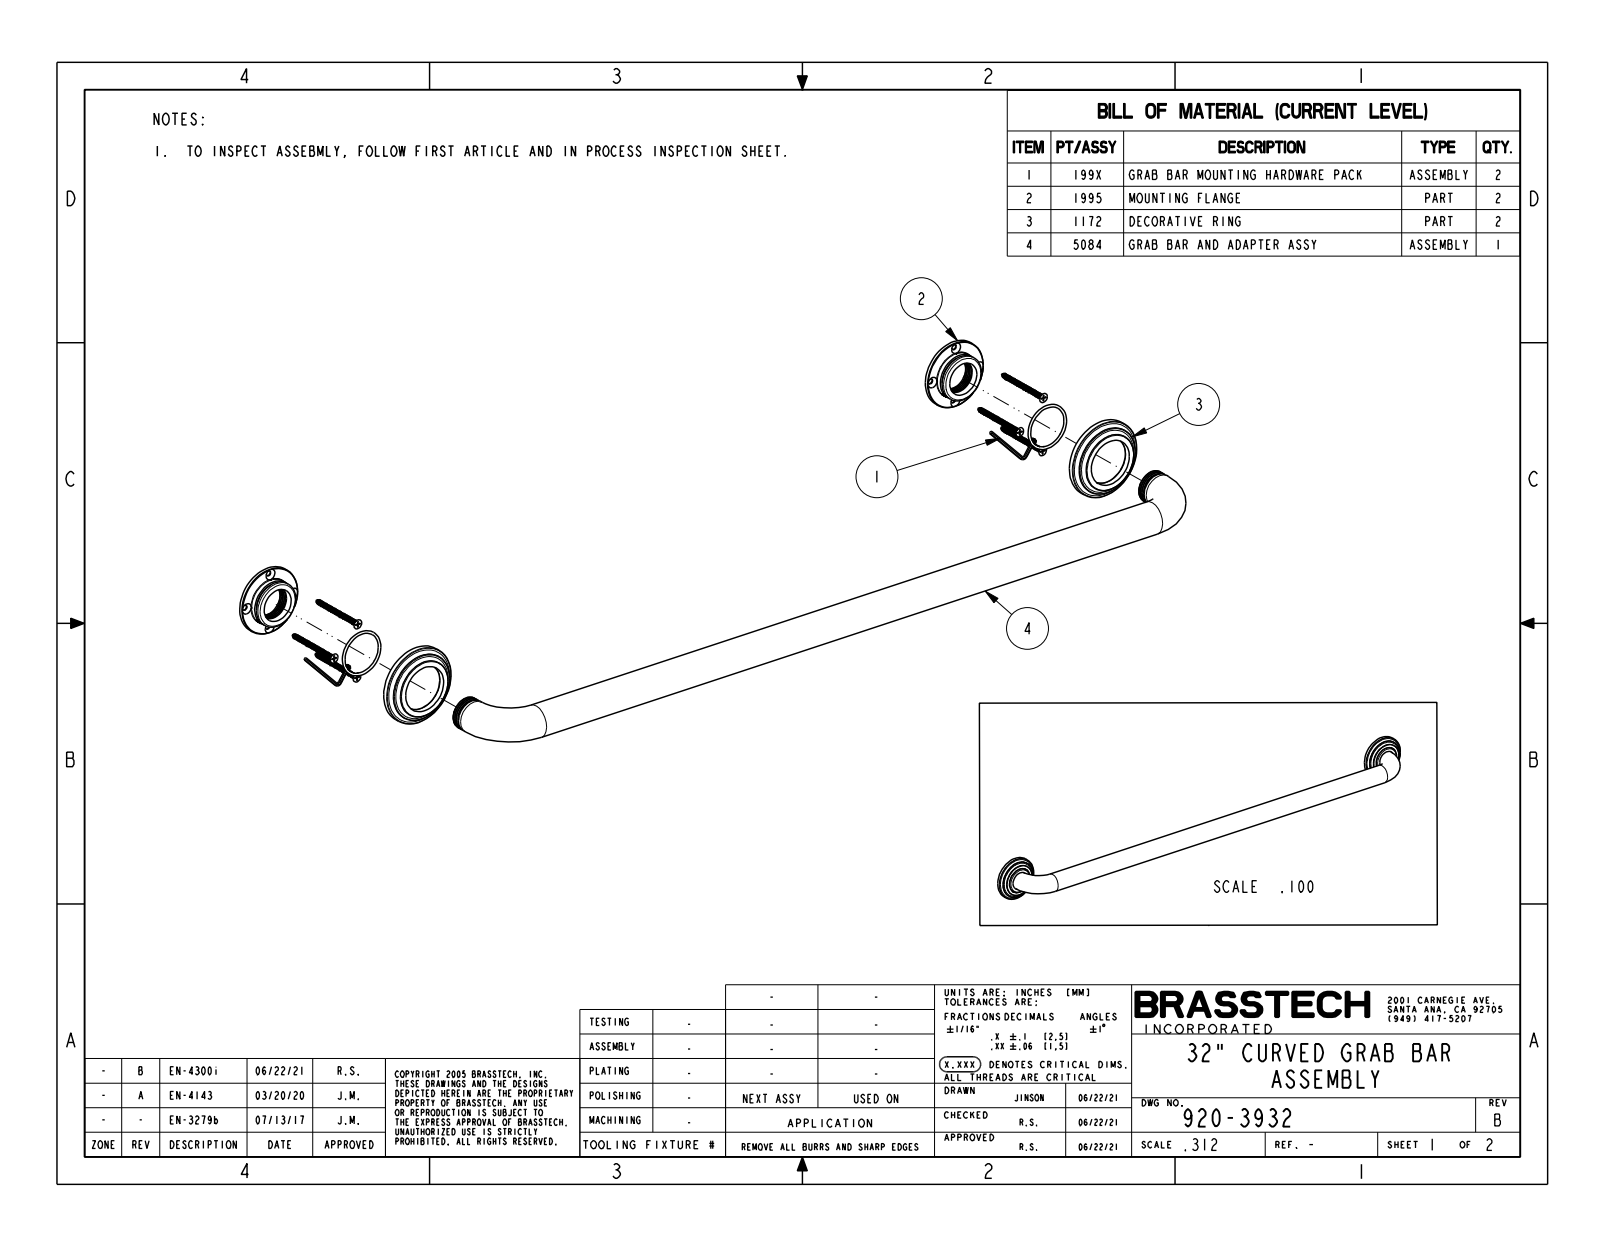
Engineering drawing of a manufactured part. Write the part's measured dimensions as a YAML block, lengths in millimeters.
part_name: "1995; 20-287_ASM; 80530; 50869 (+3 more)"
step_written_by: "PRO/ENGINEER BY PARAMETRIC TECHNOLOGY CORPORATION, 2013150 (CONFIG_CONTROL_DESIGN)"
units: millimeters
bodies: {solids: 7, faces: 676, planar: 160, cylindrical: 204, other: 312}
overall_size: [889, 76.2, 69.9]
volume: 167500
surface_area: 319000
round_holes:
  - {diameter: 5.1, count: 8}
  - {diameter: 29.3, count: 3}
  - {diameter: 4.1, count: 2}
  - {diameter: 22, count: 2}
  - {diameter: 29.5, count: 2}
  - {diameter: 32, count: 2}
  - {diameter: 45, count: 2}
  - {diameter: 72.2, count: 2}
round_bosses_or_shafts:
  - {diameter: 31.8, count: 3}
  - {diameter: 76.2, count: 2}
  - {diameter: 66, count: 2}
  - {diameter: 55.9, count: 2}
  - {diameter: 49, count: 2}
  - {diameter: 44.5, count: 2}
  - {diameter: 40.5, count: 2}
  - {diameter: 31.4, count: 2}
partial_cylinders:
  - {radius: 5.4, count: 8}
  - {radius: 1, count: 2}
face_to_face_distances: [3.8, 9.5, 13.3, 1.9, 11.4, 4.2, 15.2, 8.9, 2.5, 6.1]
hole_center_spacings: [27.6, 39.1, 812.8, 55.2, 785.7, 813.3, 840.9, 785.2]
